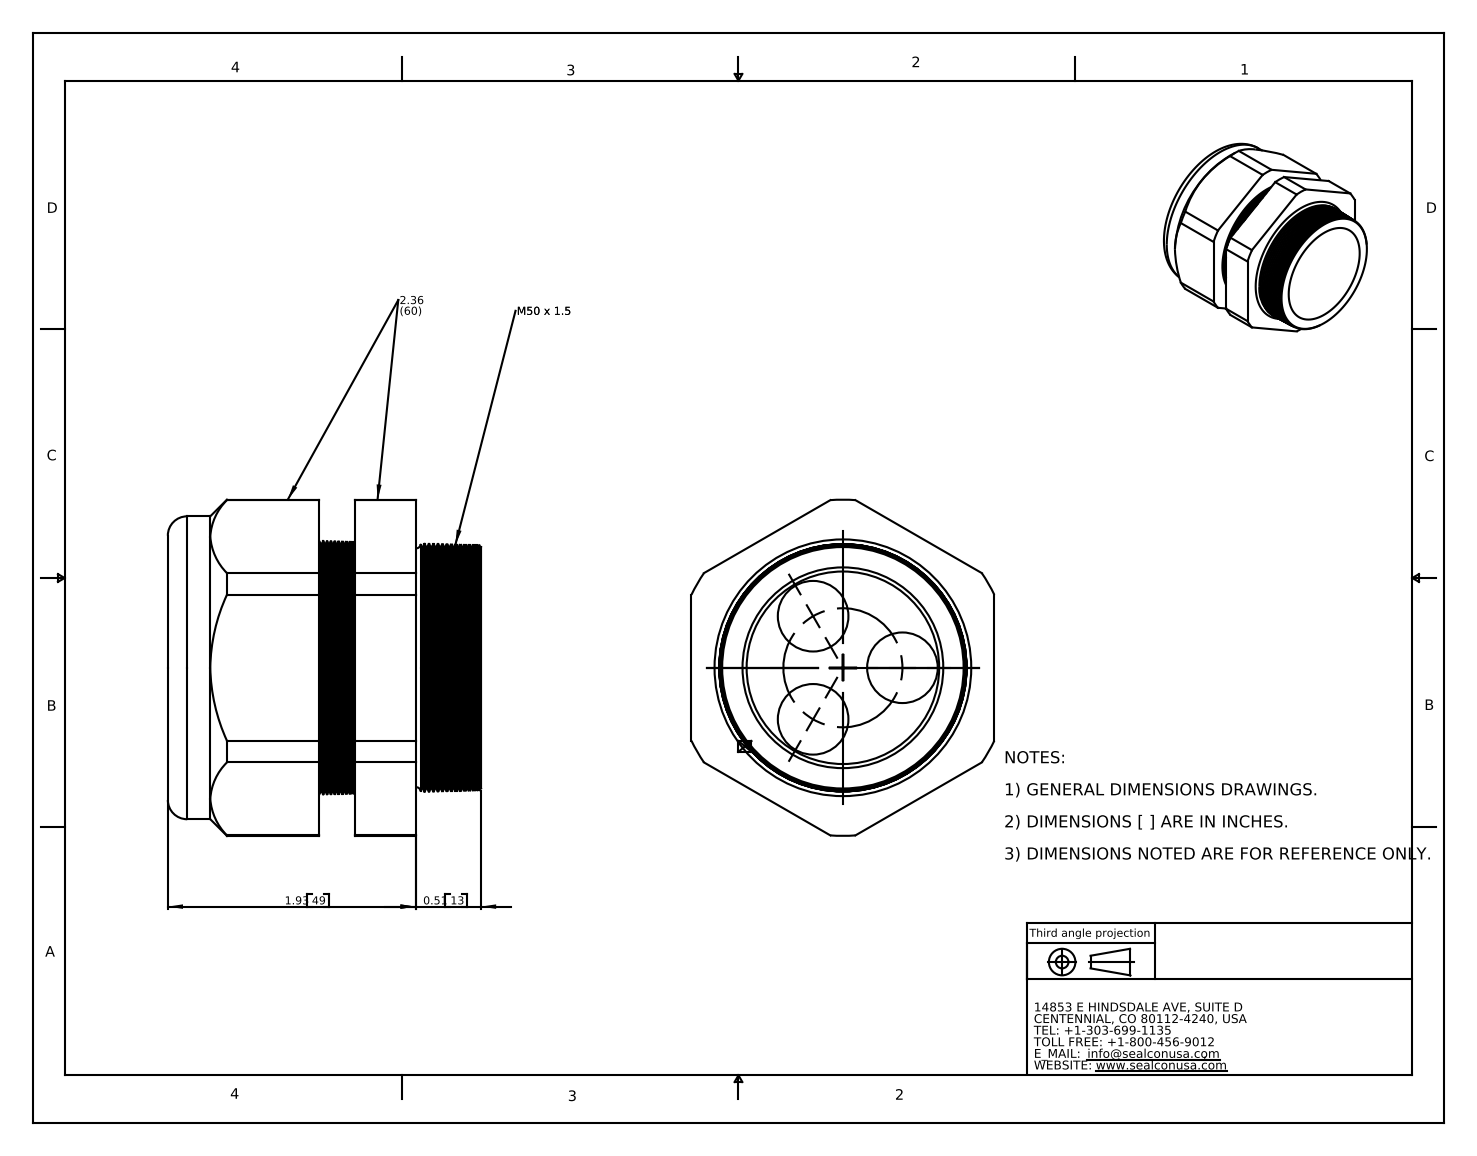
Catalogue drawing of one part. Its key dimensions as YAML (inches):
part_name: "CD50M1-GY"
step_written_by: "SolidWorks 2007 (CONFIG_CONTROL_DESIGN)"
units: inches
bodies: {solids: 2, faces: 196, planar: 20, cylindrical: 26, other: 150}
overall_size: [2.62, 2.44, 2.36]
volume: 6.03
surface_area: 48.47
round_holes:
  - {diameter: 0.55, count: 3}
  - {diameter: 1.48, count: 1}
  - {diameter: 1.5, count: 1}
round_bosses_or_shafts:
  - {diameter: 2.36, count: 1}
partial_cylinders:
  - {radius: 1.31, count: 1}
face_to_face_distances: [2.36, 0.276, 0.749, 0.472, 1.181, 1.458, 1.93, 0.45, 0.731, 1.008]
hole_center_spacings: [0.464, 0.803]
